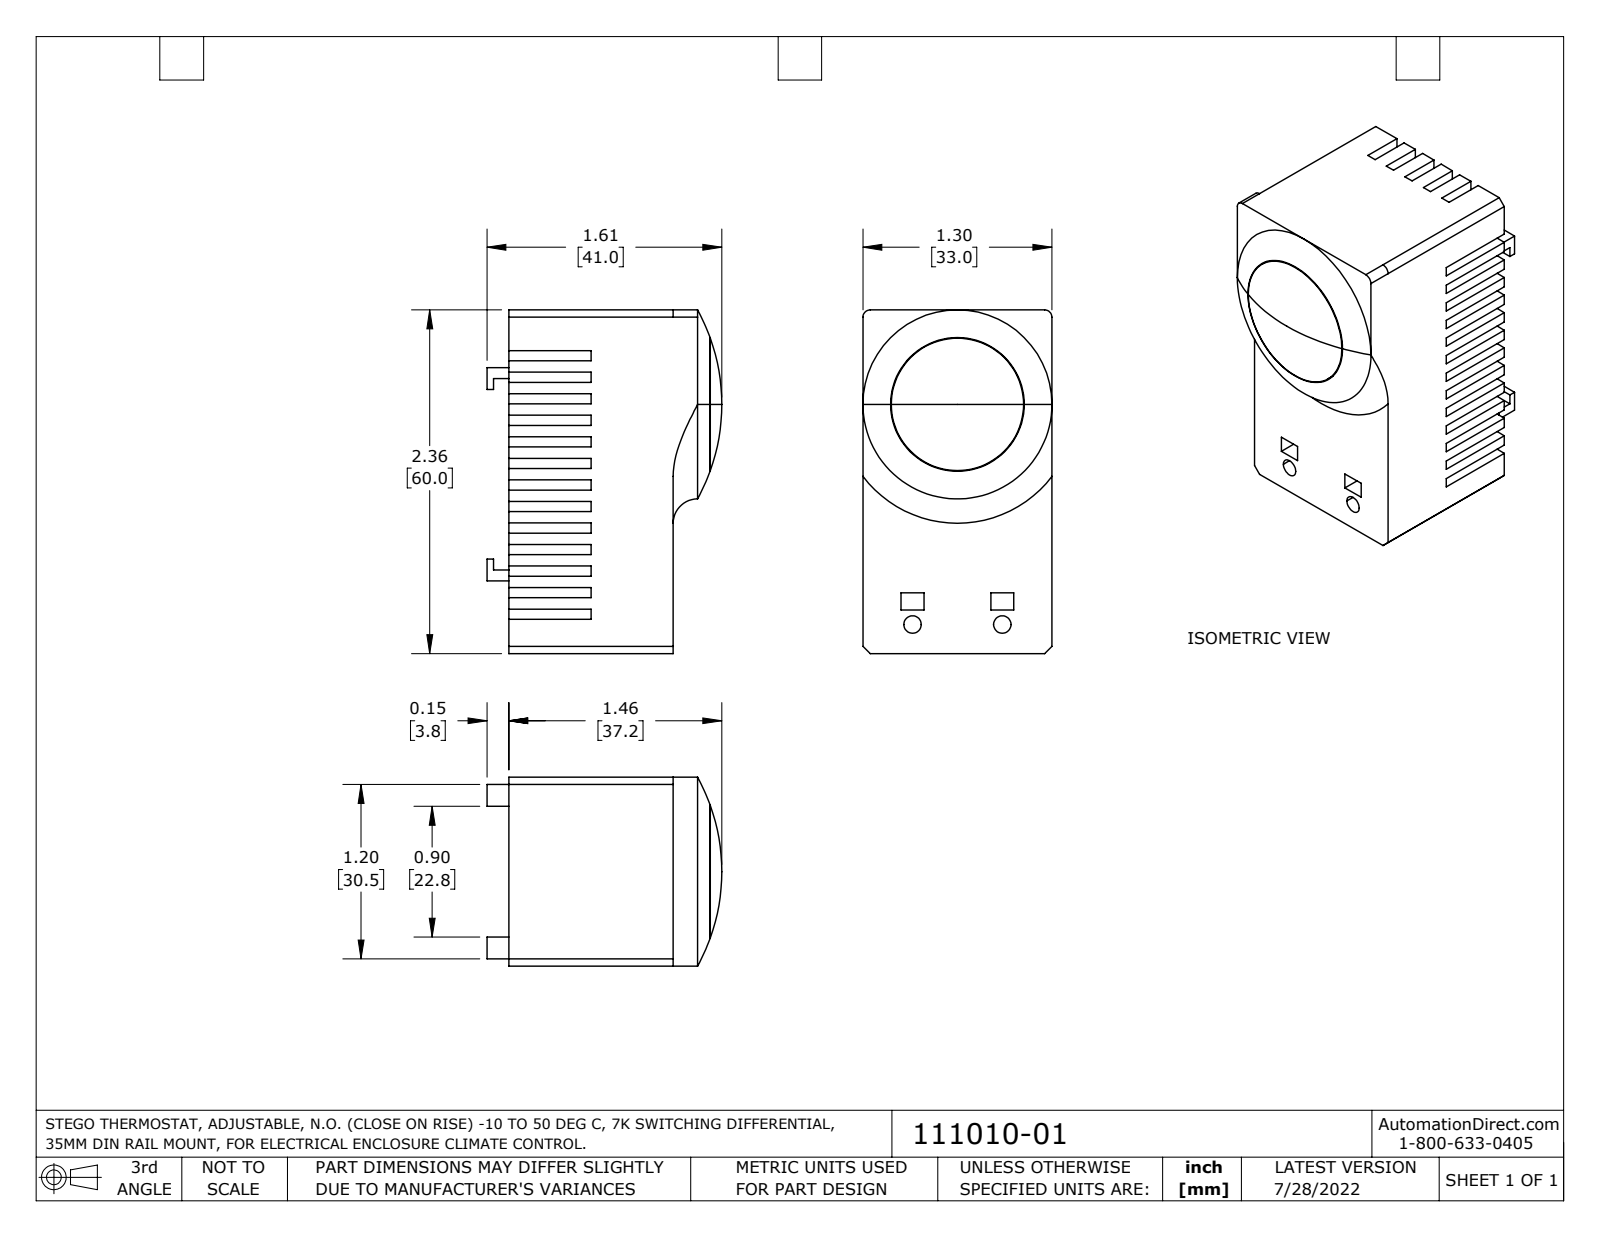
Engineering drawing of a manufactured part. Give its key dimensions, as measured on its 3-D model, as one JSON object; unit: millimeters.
{"part_name": "111010-01_Default", "step_written_by": "SolidWorks 2021 (CONFIG_CONTROL_DESIGN)", "units": "millimeters", "bodies": {"solids": 1, "faces": 198, "planar": 183, "cylindrical": 10, "other": 5}, "overall_size": [60, 41, 33], "volume_mm3": 61240, "surface_area_mm2": 12850, "round_holes": [[3, 2], [23.3, 1]], "round_bosses_or_shafts": [[23.1, 1]], "partial_cylinders_radius": [[1.3, 2]], "face_to_face_distances": [33, 3.8, 1.8, 60, 7.5, 28.7, 11.3, 15, 2, 5.5], "hole_center_spacings": [39.2, 15.7]}
